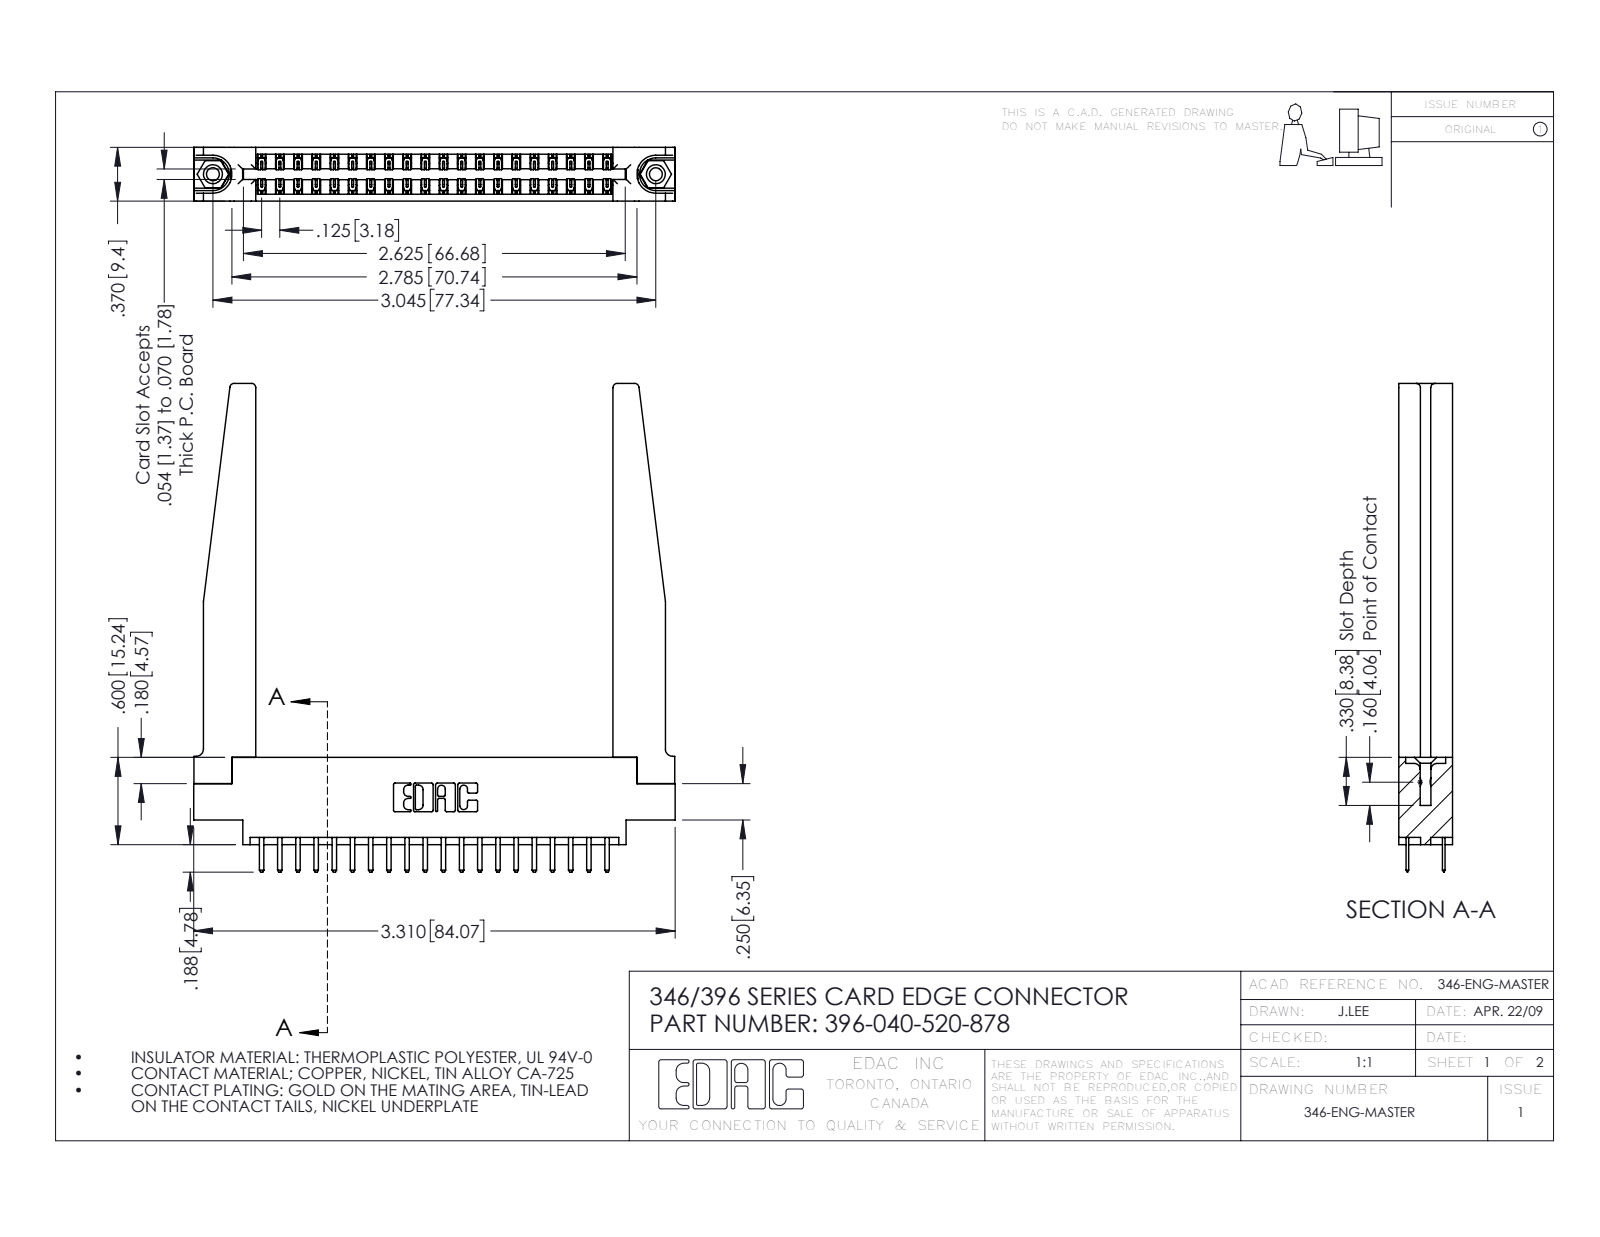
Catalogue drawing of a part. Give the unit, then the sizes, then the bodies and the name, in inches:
Units: inches
Overall size (bounding box): 3.358 × 3.31 × 0.37
Round holes (diameter × count): ⌀0.089 ×2, ⌀0.125 ×2, ⌀0.156 ×2, ⌀0.064 ×1
Round bosses / shafts (diameter × count): ⌀0.155 ×2
Partial cylindrical surfaces — rounded edges, fillets, slot ends (radius × count): R0.006 ×60, R0.01 ×44, R0.01 ×22, R0.03 ×8, R0.007 ×6, R0.031 ×6, R0.026 ×3, R0.014 ×2
Main face-to-face distances: 0.37, 0.048, 0.322, 0.072, 0.148, 0.15, 0.25, 0.298, 0.025, 0.275
Hole centre spacings: 0.246, 2.837, 3.045
Volume: 0.901 in³ · Surface area: 26.55 in²
Bodies: 45 solids, 2600 faces (1702 planar, 846 cylindrical, 52 other)
Part name (STEP PRODUCT): 345-250-001_345-250-001-102; 346-220-078_345-220-078; 345-292-001_345-293-120; 396-040-520-878 (+1 more)
STEP written by: SolidWorks 2016 (CONFIG_CONTROL_DESIGN)
